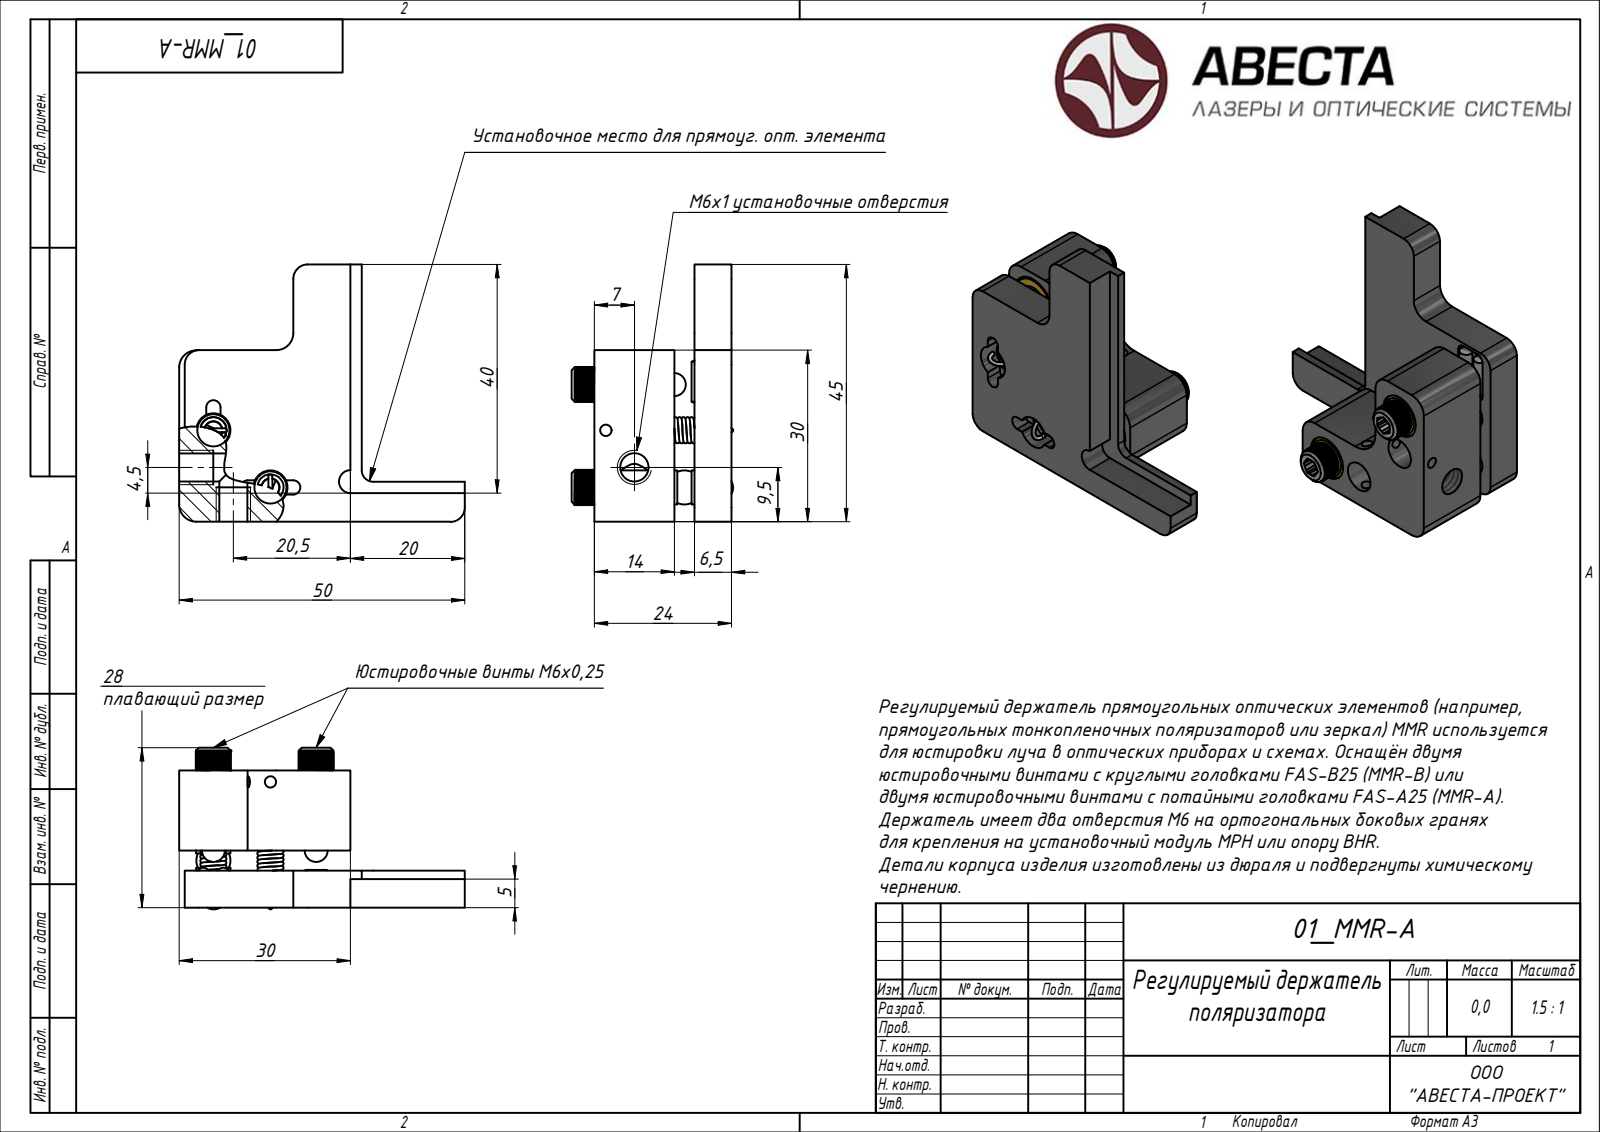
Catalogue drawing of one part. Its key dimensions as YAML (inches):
step_written_by: "ST-DEVELOPER v15 (AUTOMOTIVE_DESIGN)"
units: inches
bodies: {solids: 12, faces: 253, planar: 99, cylindrical: 0, other: 154}
overall_size: [1.969, 1.772, 1.047]
volume: 0.865
surface_area: 16.79
face_to_face_distances: [0.256, 0.394, 0.138, 1.181, 0.472, 0.945, 0.689, 0.551, 0.197, 0.709]
